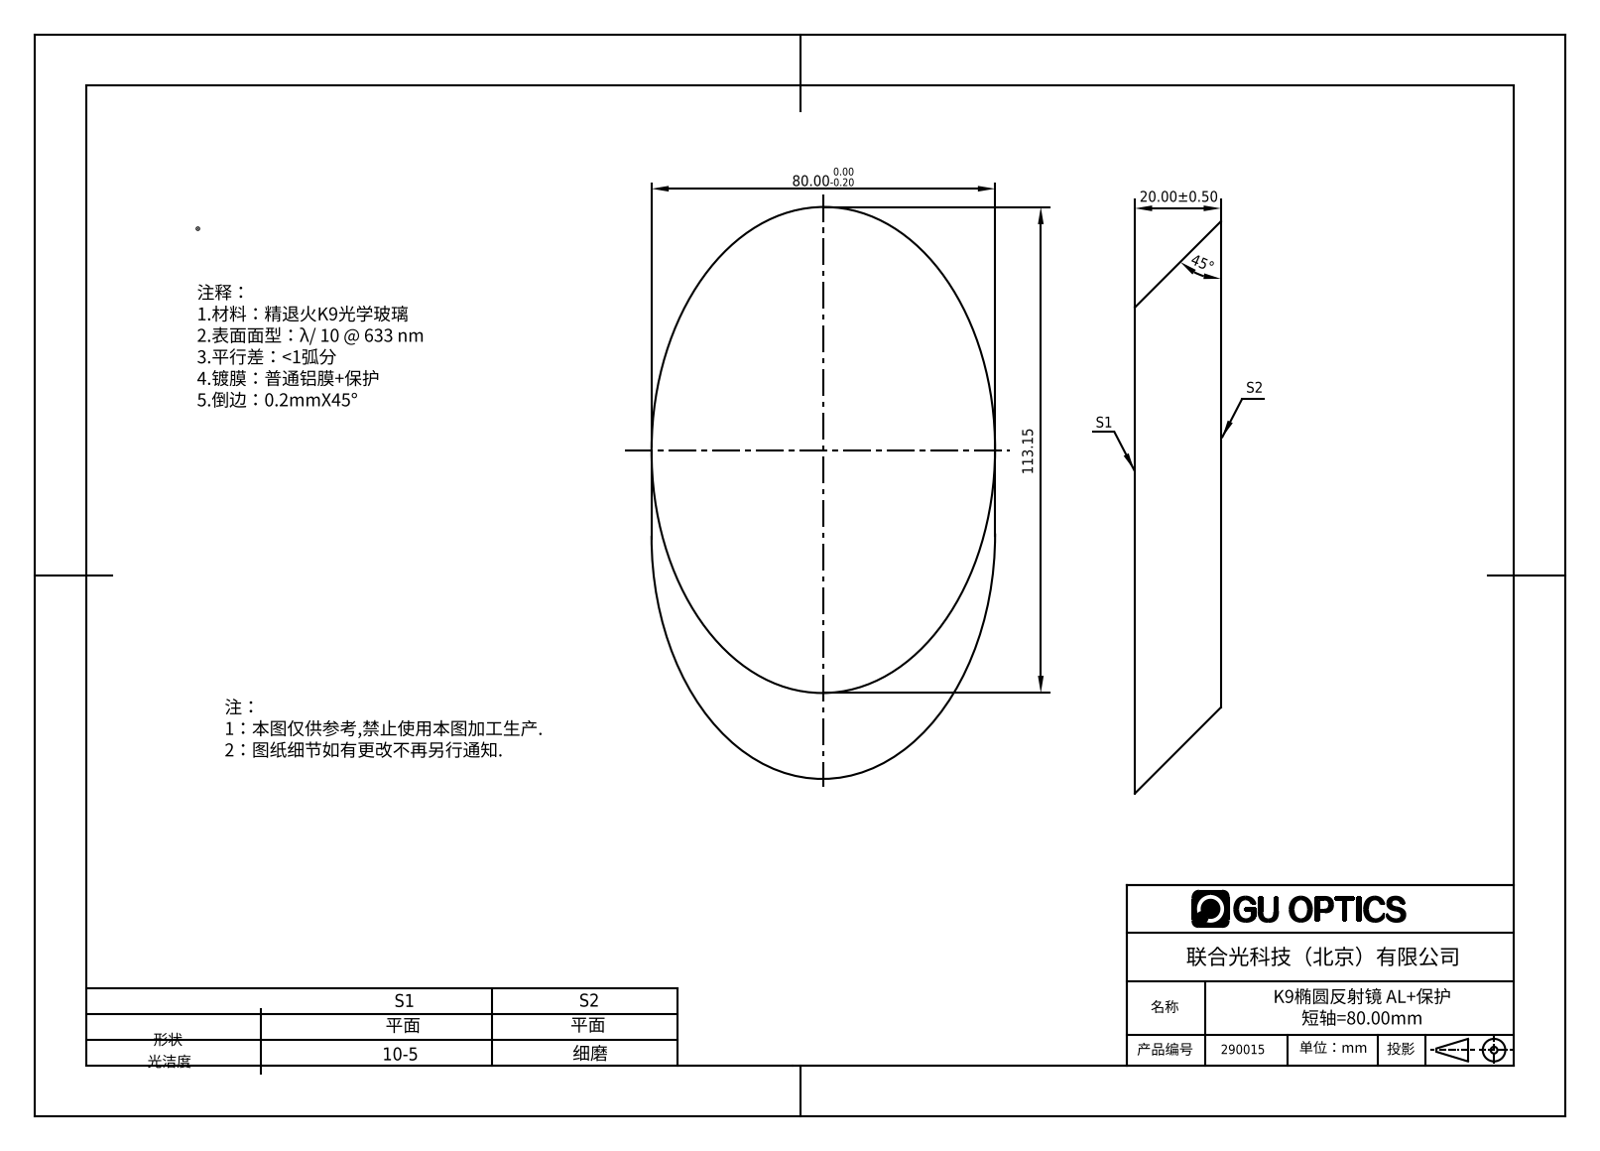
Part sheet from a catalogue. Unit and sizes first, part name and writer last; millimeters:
Units: millimetres
Overall size (bounding box): 133.15 × 80 × 20
Main face-to-face distances: 20
Volume: 143 249 mm³ · Surface area: 21 339 mm²
Bodies: 1 solid, 3 faces (2 planar, 0 cylindrical, 1 other)
Part name (STEP PRODUCT): 290007
STEP written by: SolidWorks 2020 (CONFIG_CONTROL_DESIGN)
